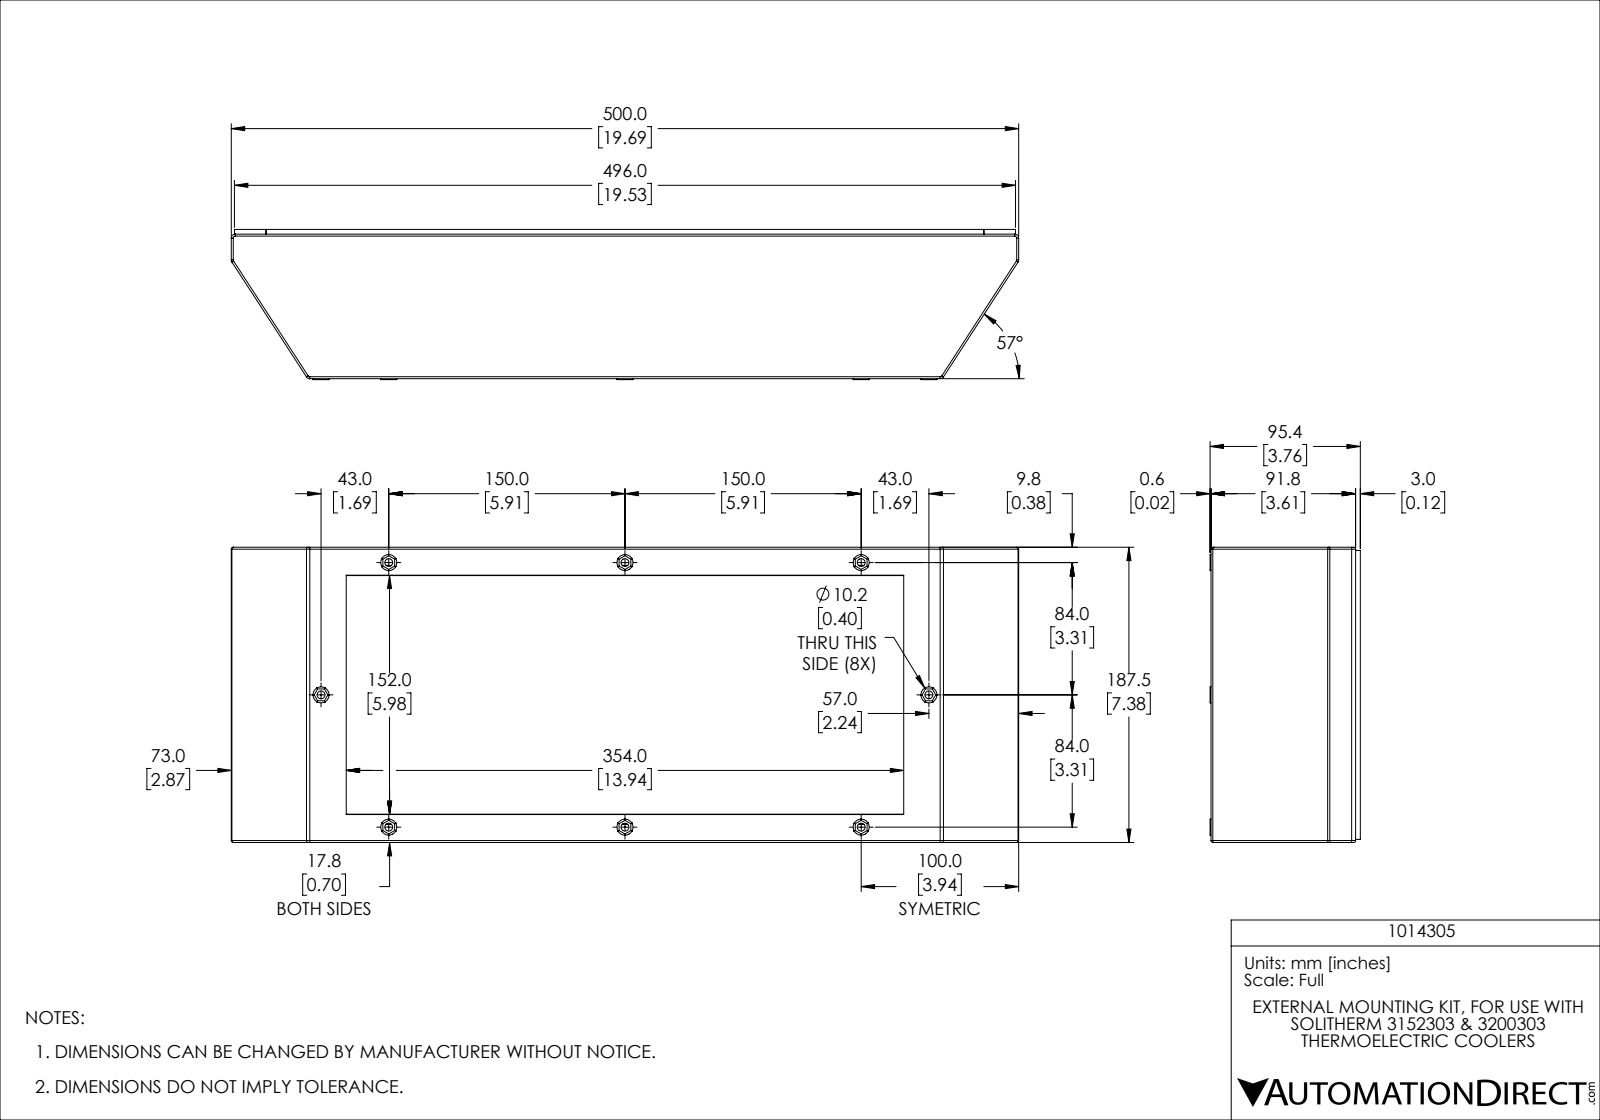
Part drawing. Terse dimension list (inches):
name: 1014305
written by: SolidWorks 2019 (AUTOMOTIVE_DESIGN)
unit: in
bodies: 1 solid, 931 faces (815 planar, 72 cylindrical, 44 other)
size: 19.685 × 7.382 × 3.756
volume: 88.98 in³; area: 624.9 in²
holes: 10× ⌀0.197, 8× ⌀0.315
bosses: 10× ⌀0.35, 8× ⌀0.402
rounds: 12× R0.049, 6× R0.039, 6× R0.098
face distances: 0.453, 6.929, 7.382, 6.476, 0.059, 3.555, 0.177, 3.732, 3.28, 3.102
hole spacings: 3.715, 4.876, 5.906, 8.287, 8.867, 10.048, 13.903, 15.745
